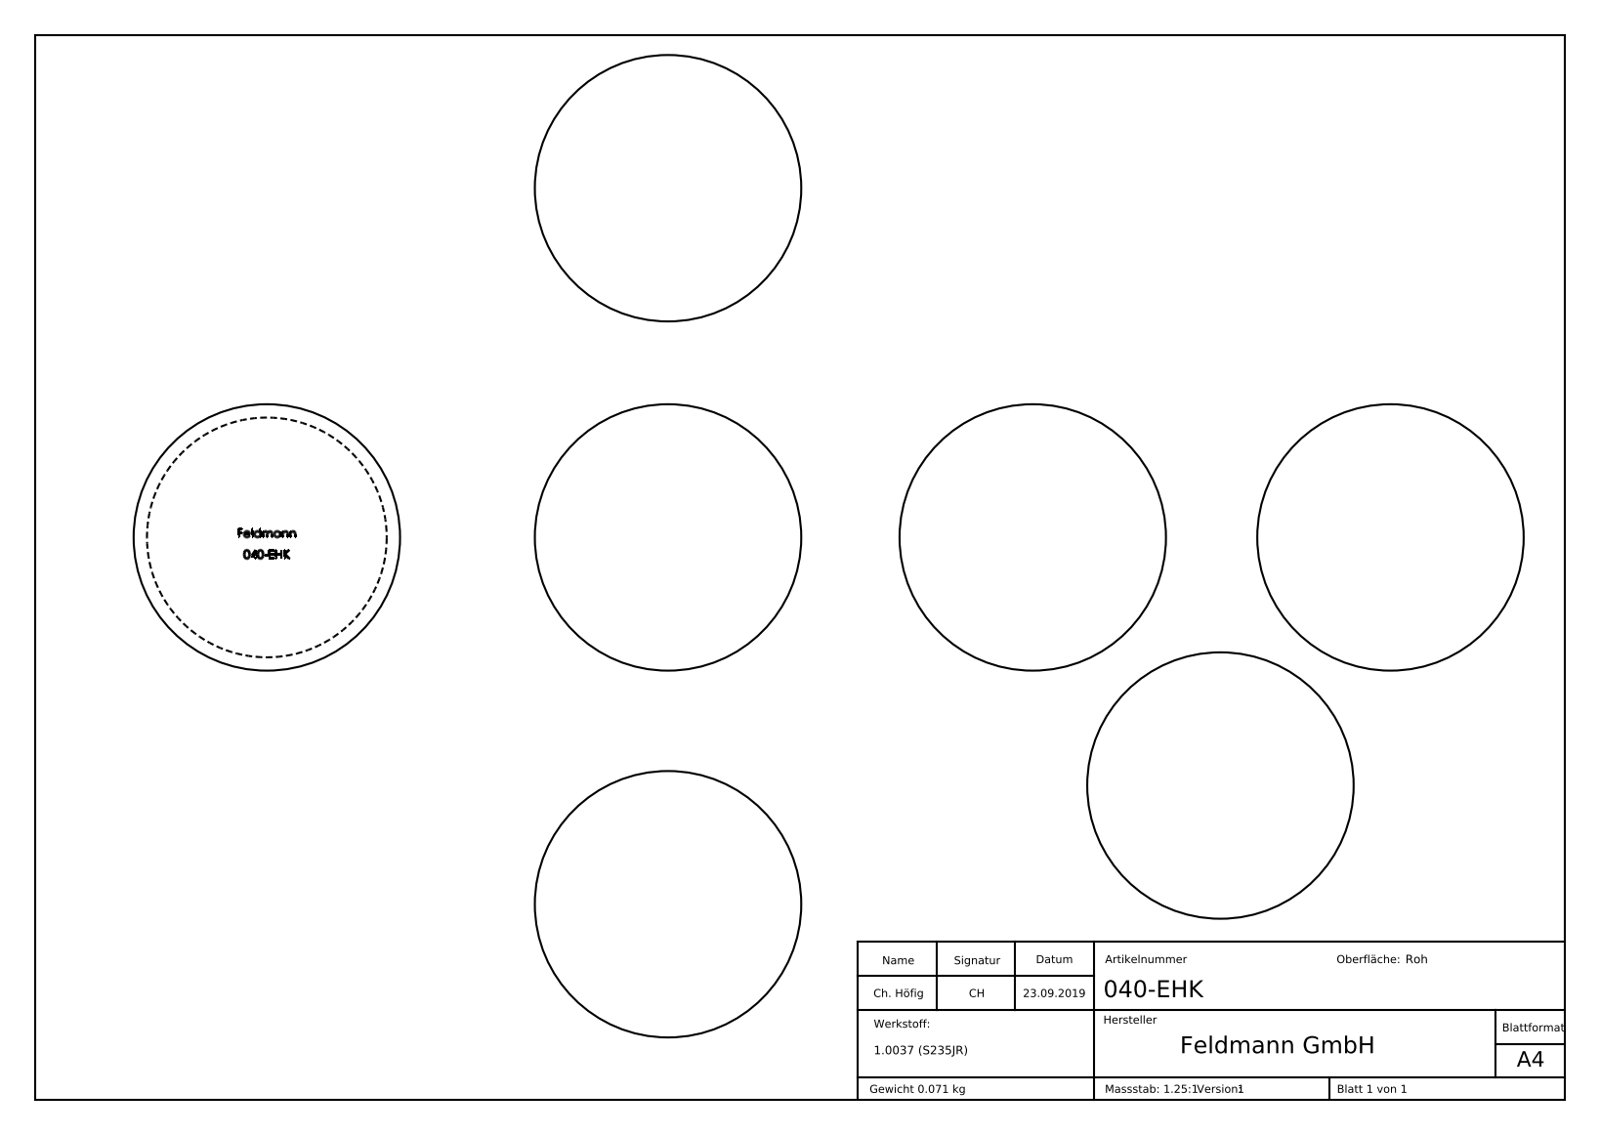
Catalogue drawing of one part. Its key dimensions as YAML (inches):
part_name: "040-EHK"
step_written_by: "SolidWorks 2015 (CONFIG_CONTROL_DESIGN)"
units: inches
bodies: {solids: 1, faces: 199, planar: 106, cylindrical: 0, other: 93}
overall_size: [1.575, 1.575, 1.575]
volume: 0.554
surface_area: 14.12
face_to_face_distances: [0.177, 0.018, 0.126, 0.05, 0.023, 0.172, 0.08, 0.013, 0.102, 0.141]
